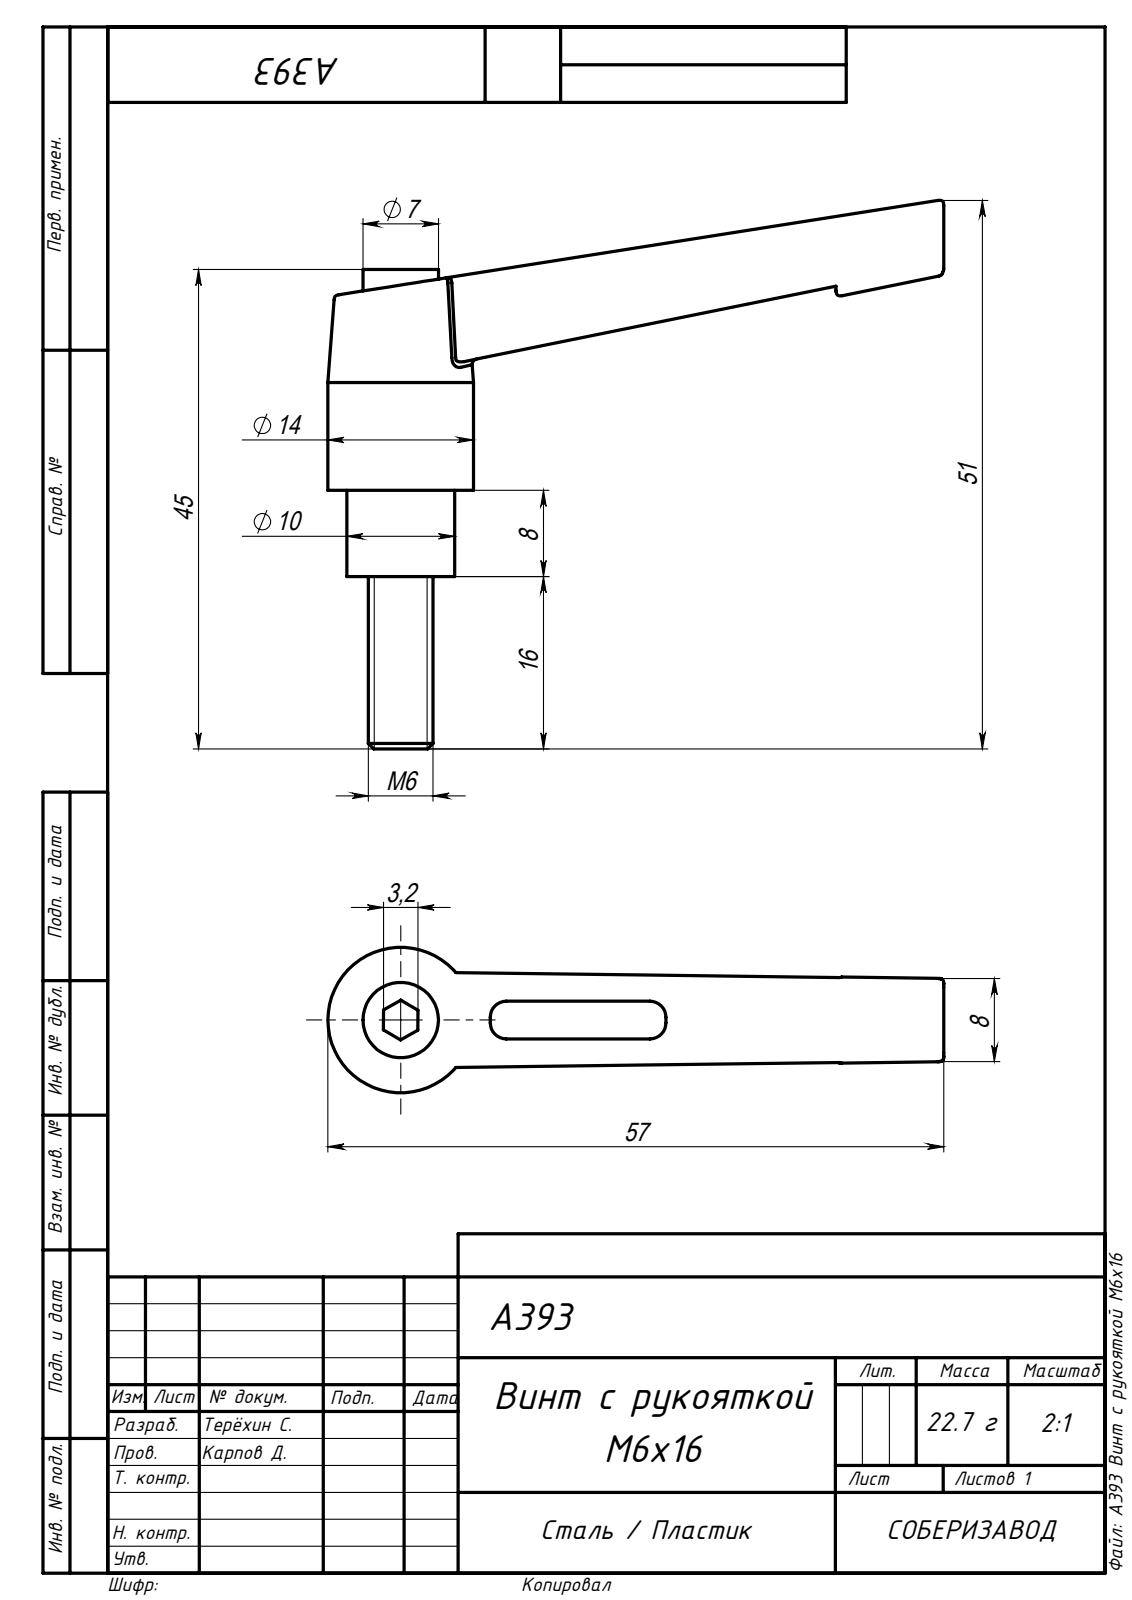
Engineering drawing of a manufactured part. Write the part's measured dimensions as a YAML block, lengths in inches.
part_name: "A393 Винт с рукояткой М6х16"
step_written_by: "SolidWorks 2020 (AUTOMOTIVE_DESIGN)"
units: inches
bodies: {solids: 1, faces: 79, planar: 29, cylindrical: 12, other: 38}
overall_size: [2.249, 2.005, 0.531]
volume: 0.306
surface_area: 5.273
round_bosses_or_shafts:
  - {diameter: 0.531, count: 1}
  - {diameter: 0.394, count: 1}
  - {diameter: 0.276, count: 1}
  - {diameter: 0.236, count: 1}
partial_cylinders:
  - {radius: 0.059, count: 4}
face_to_face_distances: [0.236, 0.315, 1.311, 1.122, 0.807, 0.63, 0.945, 1.752, 0.126, 1.634]
